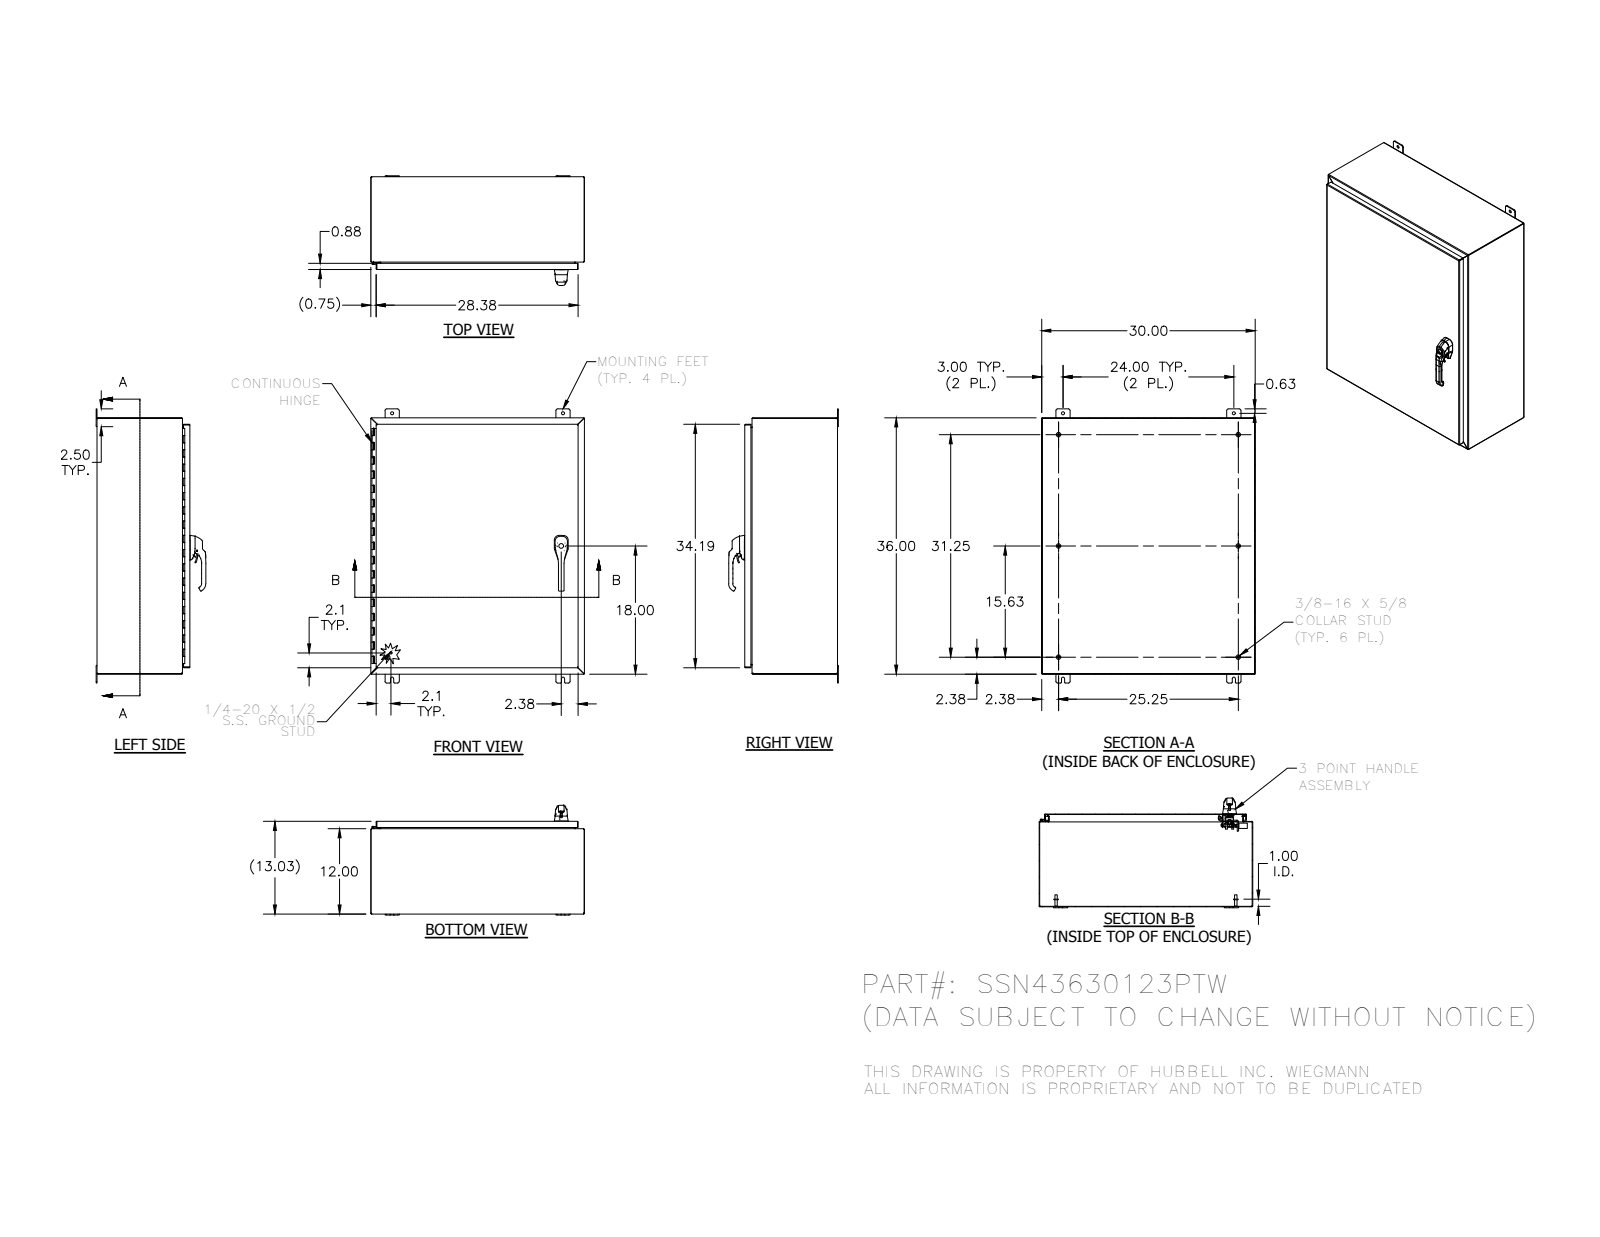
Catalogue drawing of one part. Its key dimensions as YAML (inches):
part_name: "DIN985_M10; 34x28; PLASTIC-ROLLER-CAM_AF1; DIN3771_16X2_5 (+8 more)"
step_written_by: "SolidWorks 2014 (AUTOMOTIVE_DESIGN)"
units: inches
bodies: {solids: 58, faces: 3221, planar: 1088, cylindrical: 1344, other: 789}
overall_size: [38.5, 30, 15.408]
volume: 331.6
surface_area: 8682
round_holes:
  - {diameter: 0.262, count: 8}
  - {diameter: 0.187, count: 4}
  - {diameter: 0.438, count: 4}
  - {diameter: 0.213, count: 3}
  - {diameter: 0.281, count: 3}
  - {diameter: 0.241, count: 2}
  - {diameter: 0.25, count: 2}
  - {diameter: 0.252, count: 2}
  - {diameter: 0.315, count: 2}
  - {diameter: 0.4, count: 2}
  - {diameter: 0.402, count: 2}
  - {diameter: 0.413, count: 2}
round_bosses_or_shafts:
  - {diameter: 0.625, count: 6}
  - {diameter: 0.33, count: 6}
  - {diameter: 0.236, count: 3}
  - {diameter: 1, count: 2}
  - {diameter: 0.563, count: 2}
  - {diameter: 0.533, count: 2}
  - {diameter: 0.531, count: 2}
  - {diameter: 0.5, count: 2}
partial_cylinders:
  - {radius: 0.02, count: 172}
  - {radius: 0.012, count: 113}
  - {radius: 0.125, count: 26}
  - {radius: 0.031, count: 24}
  - {radius: 0.019, count: 21}
  - {radius: 0.105, count: 20}
  - {radius: 0.25, count: 20}
  - {radius: 0.025, count: 16}
face_to_face_distances: [0.074, 12.959, 12.885, 13.033, 29.926, 35.926, 29.852, 30, 35.852, 36]
hole_center_spacings: [0.38, 0.492, 0.76, 0.886, 26.428, 0.234, 0.258, 0.38]
